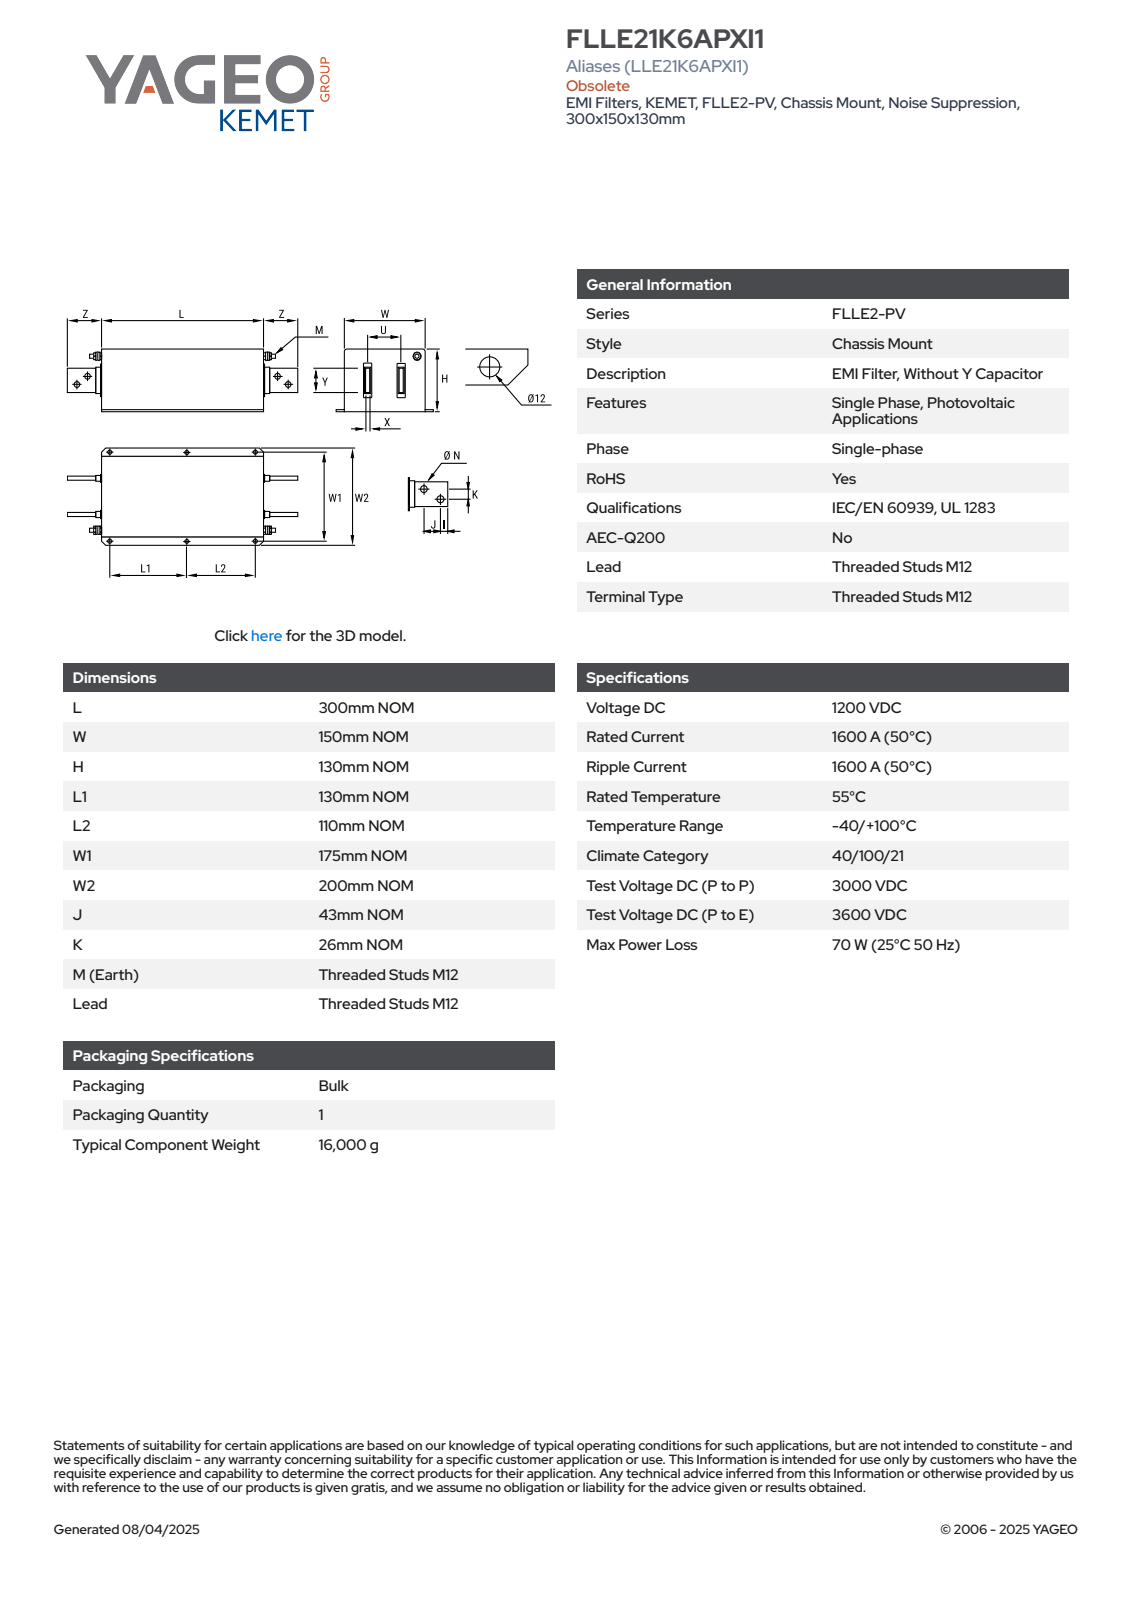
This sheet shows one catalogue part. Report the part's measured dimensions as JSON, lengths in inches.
{"part_name": "Rivet Ø3.2x4; 094-00298 Side 1600A DC RevA; Busbar 10x60^FLLE21K6APVI1_EXT; HEX BOLT M12x45_91280A722 (+8 more)", "step_written_by": "SolidWorks 2021 (AUTOMOTIVE_DESIGN)", "units": "inches", "bodies": {"solids": 56, "faces": 1879, "planar": 494, "cylindrical": 555, "other": 830}, "overall_size": [20.472, 7.874, 5.118], "volume_in3": 46.17, "surface_area_in2": 978.3, "round_holes": [[0.071, 12], [0.134, 8], [0.472, 6], [0.551, 5], [0.126, 4], [0.512, 1]], "round_bosses_or_shafts": [[0.126, 8], [0.945, 1], [0.472, 1]], "partial_cylinders_radius": [[0.079, 40], [0.039, 30], [0.02, 20], [0.01, 16], [0.098, 10], [0.059, 4], [0.118, 2], [0.138, 2]], "face_to_face_distances": [0.079, 5.827, 0.039, 5.039, 11.732, 5.118, 5.079, 5, 5.748, 5.906], "hole_center_spacings": [6.89, 1.28, 1.292, 1.385, 1.423, 1.978, 2.609, 2.617]}
